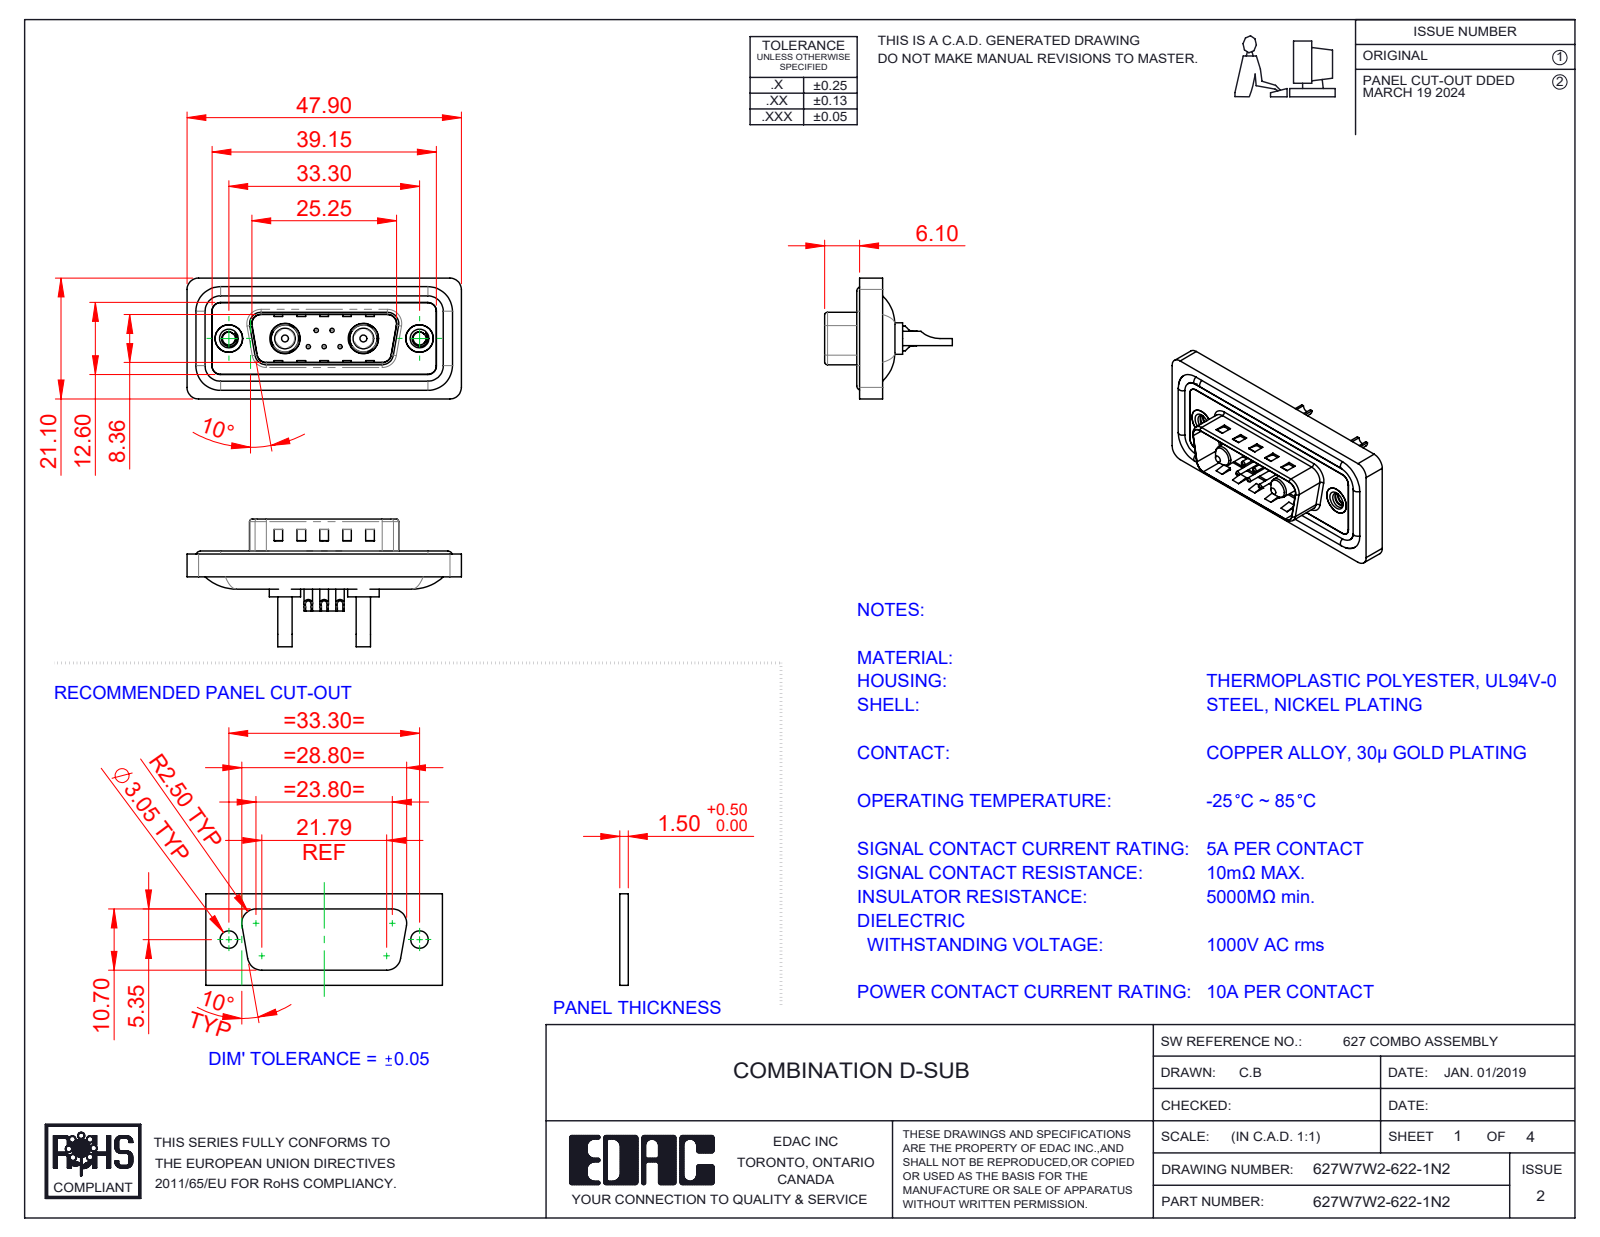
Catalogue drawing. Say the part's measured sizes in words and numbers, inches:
The part is named "627Combo Shell Rear_15 Contacts; Power Pin_10A SC; 627Combo Shell Front_15 Contacts; 627W7W2-622-1N2 (+5 more)". Its 3-D file was written by "SolidWorks 2023 (CONFIG_CONTROL_DESIGN)". It is 16 solids with 722 faces: 246 planar, 308 cylindrical and 168 other. Overall it measures 1.886 by 0.878 by 0.831 inches. Its volume is 0.337 cubic inches and its surface area 13.84 square inches. Round holes: 5 of diameter 0.03, 5 of diameter 0.039, 5 of diameter 0.063, 5 of diameter 0.079, 2 of diameter 0.067, 2 of diameter 0.089, 2 of diameter 0.157, 2 of diameter 0.189, 2 of diameter 0.191, 2 of diameter 0.197, 2 of diameter 0.209. Round bosses or shafts: 5 of diameter 0.059, 4 of diameter 0.063, 2 of diameter 0.217, 2 of diameter 0.205, 2 of diameter 0.193, 2 of diameter 0.187, 2 of diameter 0.148, 2 of diameter 0.142. Partial cylindrical surfaces (rounded edges, fillets, slot ends): 26 of radius 0.059, 20 of radius 0.079, 8 of radius 0.02, 8 of radius 0.063, 6 of radius 0.039, 4 of radius 0.01, 4 of radius 0.024, 4 of radius 0.026. The main face-to-face distances are 0.016, 0.043, 0.059, 0.063, 0.02, 0.122, 0.114, 0.157, 0.032, 0.377. The hole center spacings are 0.124, 0.109, 0.386, 0.925, 0.17, 0.17, 0.198, 0.198.
